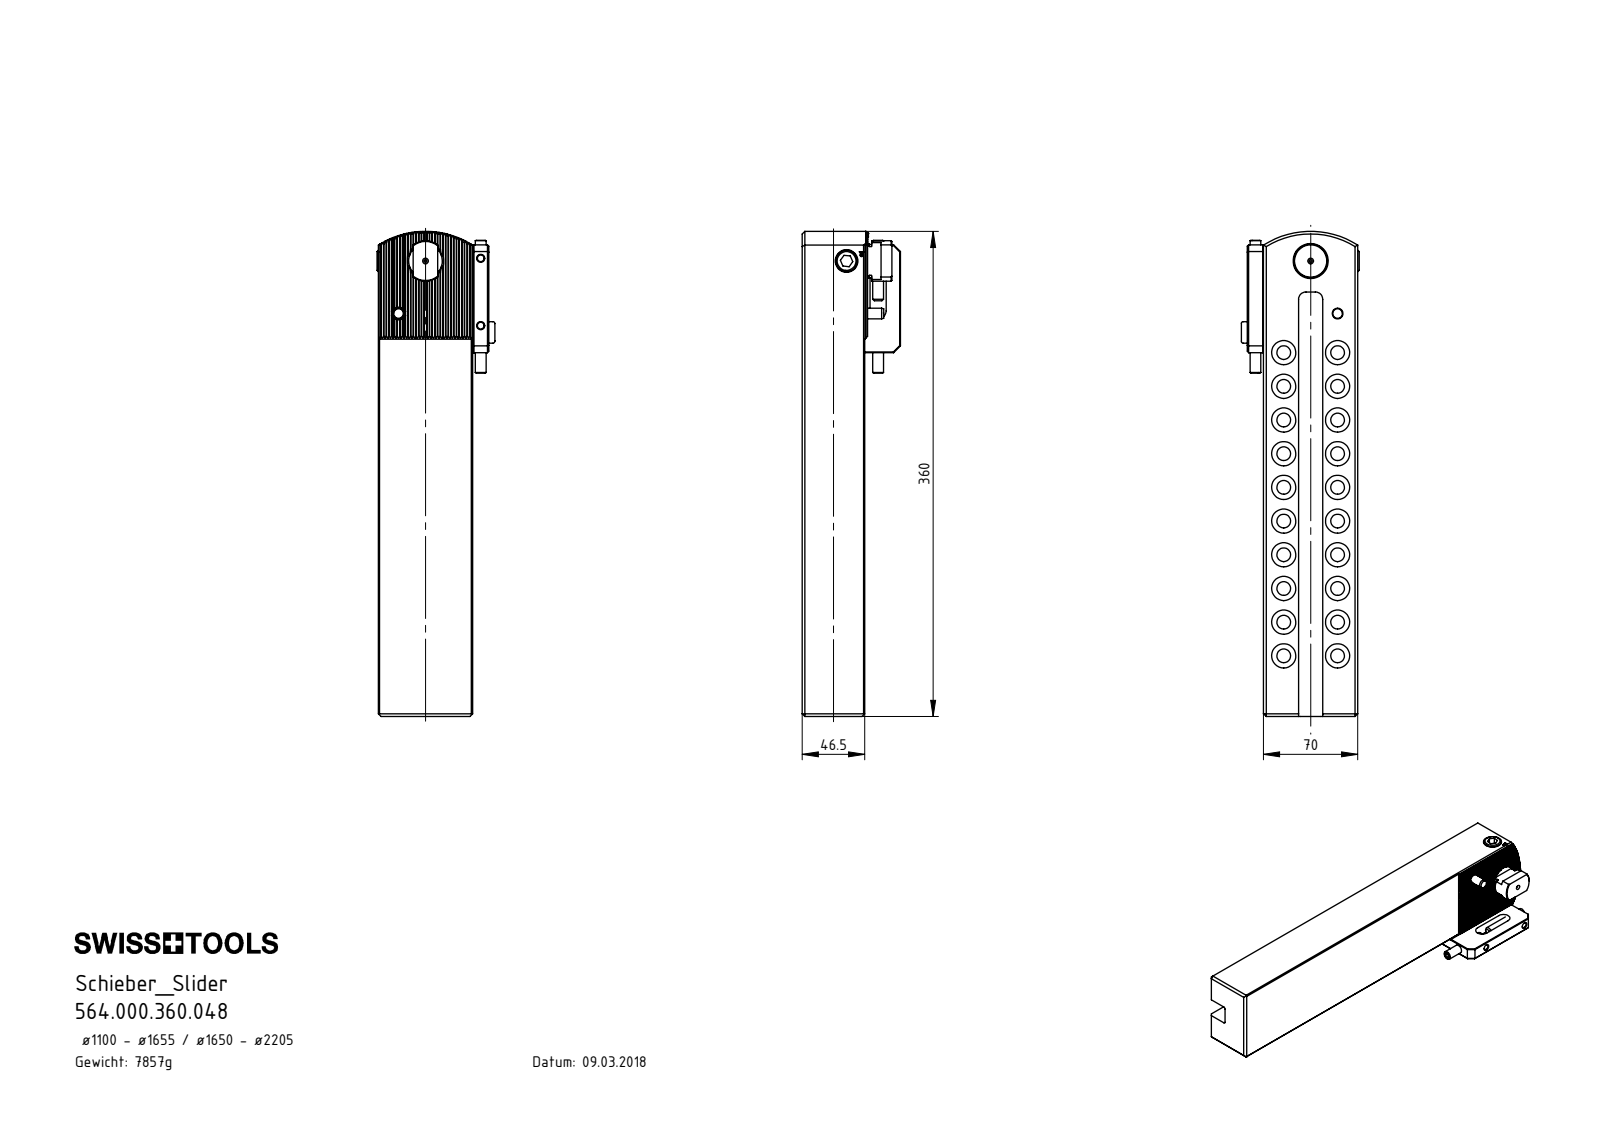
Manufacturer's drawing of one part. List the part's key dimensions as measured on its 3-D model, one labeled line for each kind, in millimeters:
Part name (STEP PRODUCT): VK1-ER2.101.010_A; ISO 4026 - M8 x 45; VK1-ER2.201.010_A_vorgespannt; ISO 4762 - M10 x 16 (+6 more)
STEP written by: SolidWorks 2017 (CONFIG_CONTROL_DESIGN)
Units: millimetres
Bodies: 10 solids, 724 faces (319 planar, 247 cylindrical, 158 other)
Overall size (bounding box): 360 × 87.5 × 73
Volume: 1 001 000 mm³ · Surface area: 162 838 mm²
Round holes (diameter × count): ⌀18 ×21, ⌀10.2 ×20, ⌀5 ×2, ⌀6 ×2, ⌀6.8 ×2, ⌀2 ×1, ⌀8 ×1, ⌀8.5 ×1, ⌀10.5 ×1, ⌀11 ×1, ⌀14 ×1, ⌀25 ×1
Round bosses / shafts (diameter × count): ⌀16 ×2, ⌀10 ×1, ⌀8 ×1
Partial cylindrical surfaces — rounded edges, fillets, slot ends (radius × count): R0.14 ×33, R2 ×4, R1.5 ×3, R5.5 ×2, R6 ×2, R12.3 ×1, R15 ×1, R65 ×1
Main face-to-face distances: 70, 46.5, 44, 26, 26.5, 18, 20, 6.5, 40, 13.5
Hole centre spacings: 25, 47.17, 50, 64.03, 75, 85, 100, 107.7
